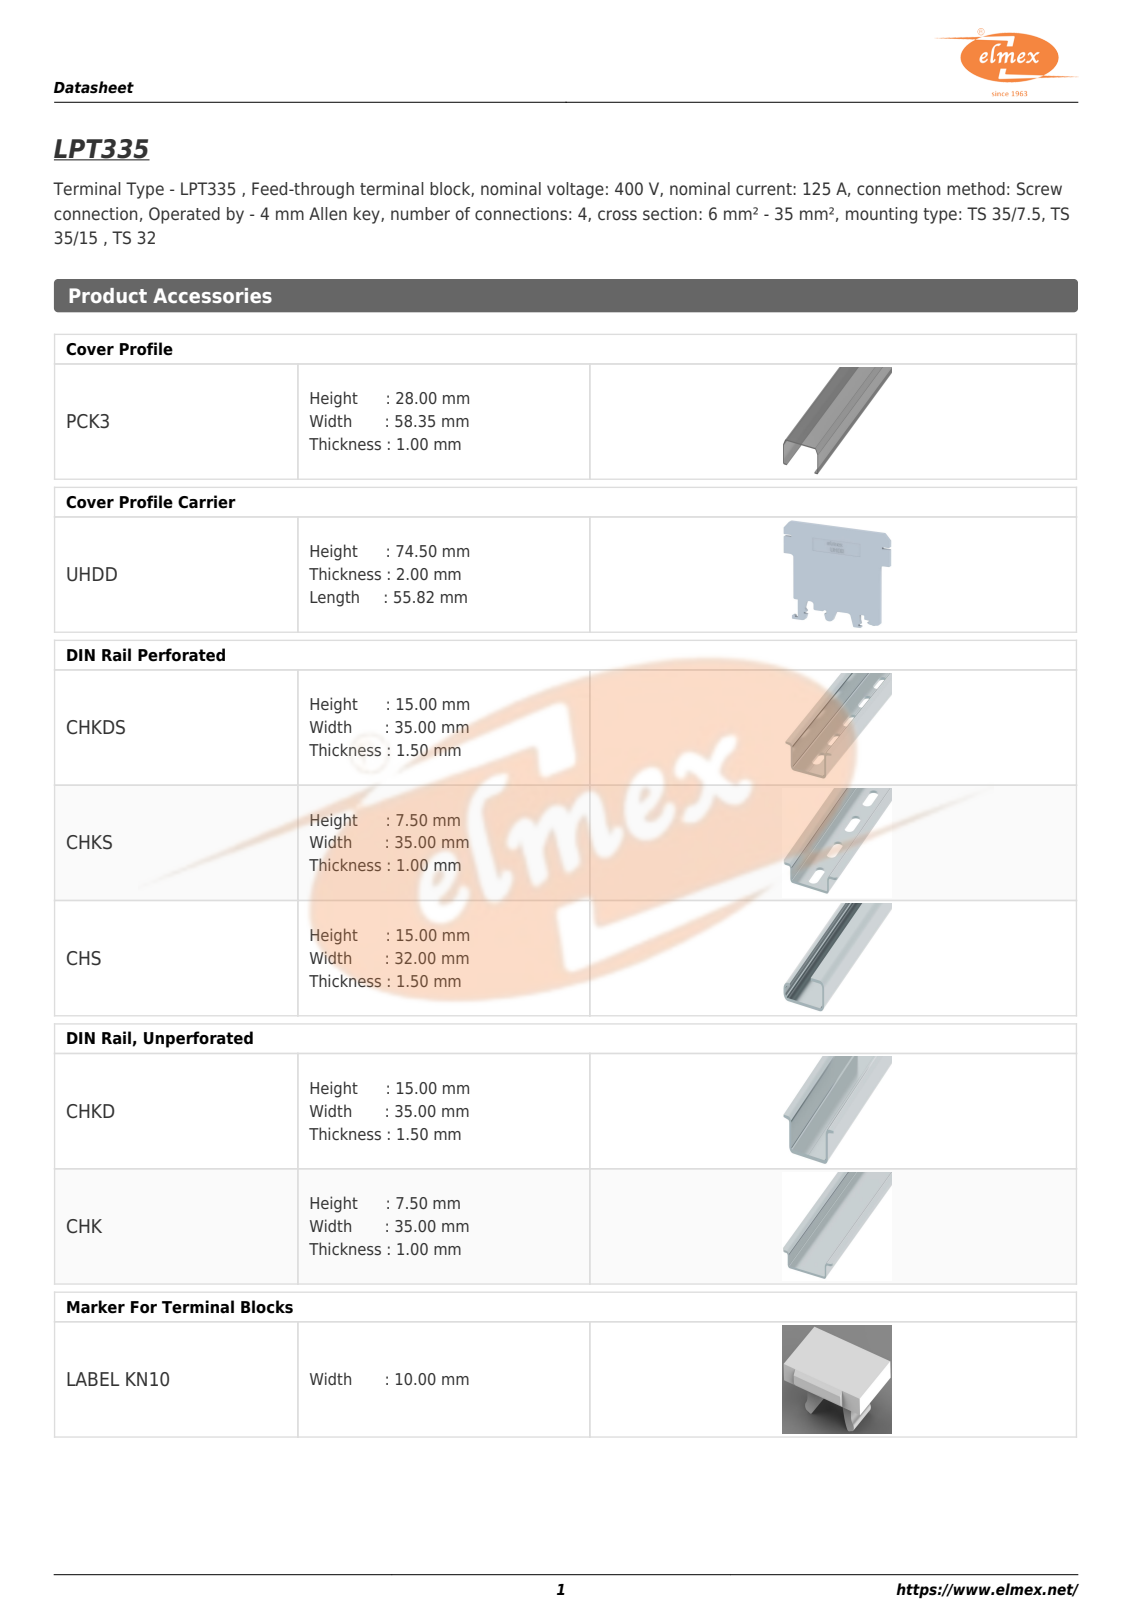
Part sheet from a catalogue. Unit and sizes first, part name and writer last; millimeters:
Units: millimetres
Overall size (bounding box): 65.55 × 53.51 × 7.15
Partial cylindrical surfaces — rounded edges, fillets, slot ends (radius × count): R0.5 ×7, R0.25 ×5, R1 ×5, R0.4 ×4, R0.75 ×2, R1.5 ×2, R2 ×2, R0.6 ×1
Main face-to-face distances: 7.15, 50.5, 3, 53.5, 2.65, 56.71, 3.65, 1, 54.06, 6
Volume: 21 519 mm³ · Surface area: 8 103 mm²
Bodies: 1 solid, 91 faces (55 planar, 36 cylindrical, 0 other)
STEP written by: ST-DEVELOPER v16 (AUTOMOTIVE_DESIGN)
